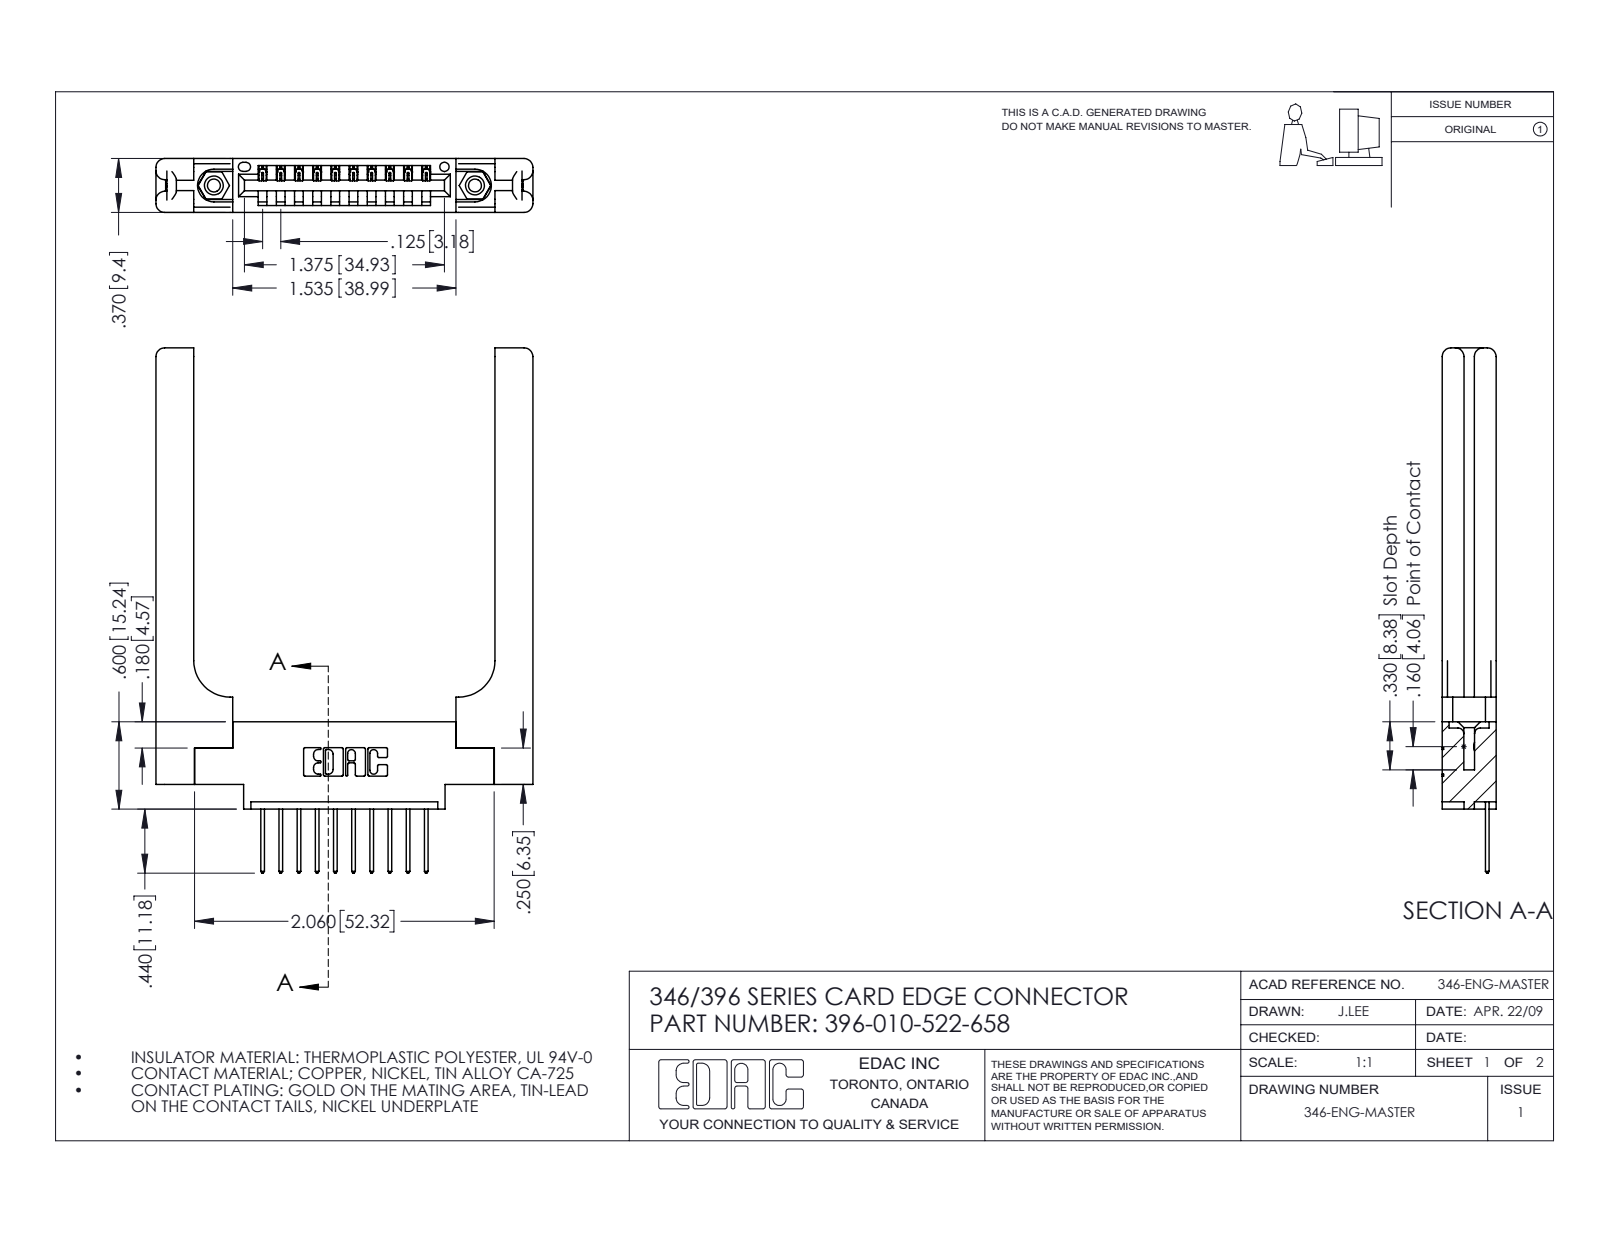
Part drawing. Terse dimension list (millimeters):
name: 346 Part_0.170 Offset - 0.156 Dia-TH; 396-010-522-658; 346-220-058_345-220-058; 345-250-001_345-250-001-102 (+1 more)
written by: SolidWorks 2016 (CONFIG_CONTROL_DESIGN)
unit: mm
bodies: 15 solids, 962 faces (628 planar, 274 cylindrical, 60 other)
size: 91.7 × 65.8 × 9.4
volume: 13 400 mm³; area: 12 430 mm²
holes: 2× ⌀2.3, 2× ⌀3.2, 2× ⌀4, 1× ⌀1.6
bosses: 2× ⌀3.9
rounds: 22× R0.3, 20× R0.2, 20× R0.3, 16× R1.5, 6× R0.2, 6× R0.8, 3× R0.7, 2× R0.8
face distances: 9.4, 3.8, 1.8, 3.8, 5.6, 1.2, 8.2, 2.6, 4.4, 6.4
hole spacings: 6.2, 40.4, 45.6
